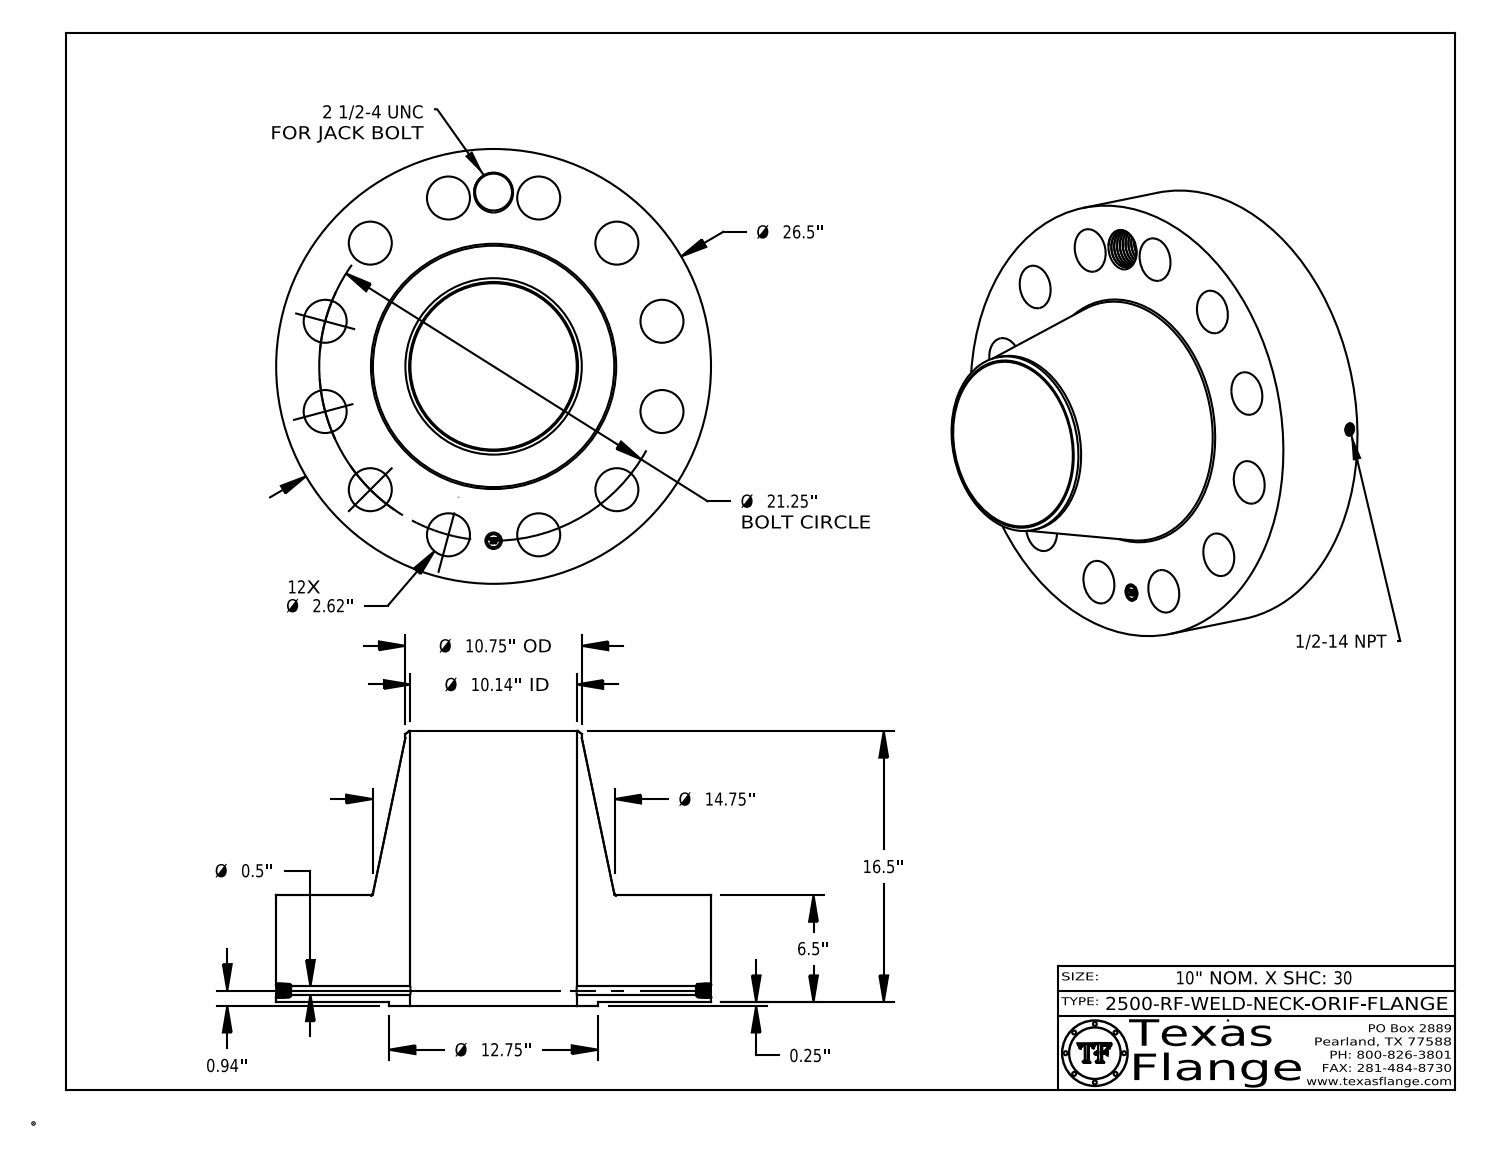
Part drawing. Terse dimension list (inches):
name: 2500-RF-WELD-NECK
written by: CATIA V5 STEP AP214 (AUTOMOTIVE_DESIGN)
unit: in
bodies: 1 solid, 843 faces (369 planar, 124 cylindrical, 350 other)
size: 26.5 × 26.5 × 16.75
volume: 3 083 in³; area: 2 949 in²
holes: 12× ⌀2.62, 1× ⌀0.5, 1× ⌀0.672, 1× ⌀1, 1× ⌀2.25, 1× ⌀10.136
bosses: 8× ⌀0.061, 1× ⌀26.5, 1× ⌀12.75, 1× ⌀10.75, 1× ⌀0.788
face distances: 6.5, 0.25, 6.75, 16.75, 16.5, 10, 0.015, 6.735, 6.485, 10.015
hole spacings: 10.625, 5.5, 15.026, 18.403, 20.526, 10.625, 21.25, 2.774
